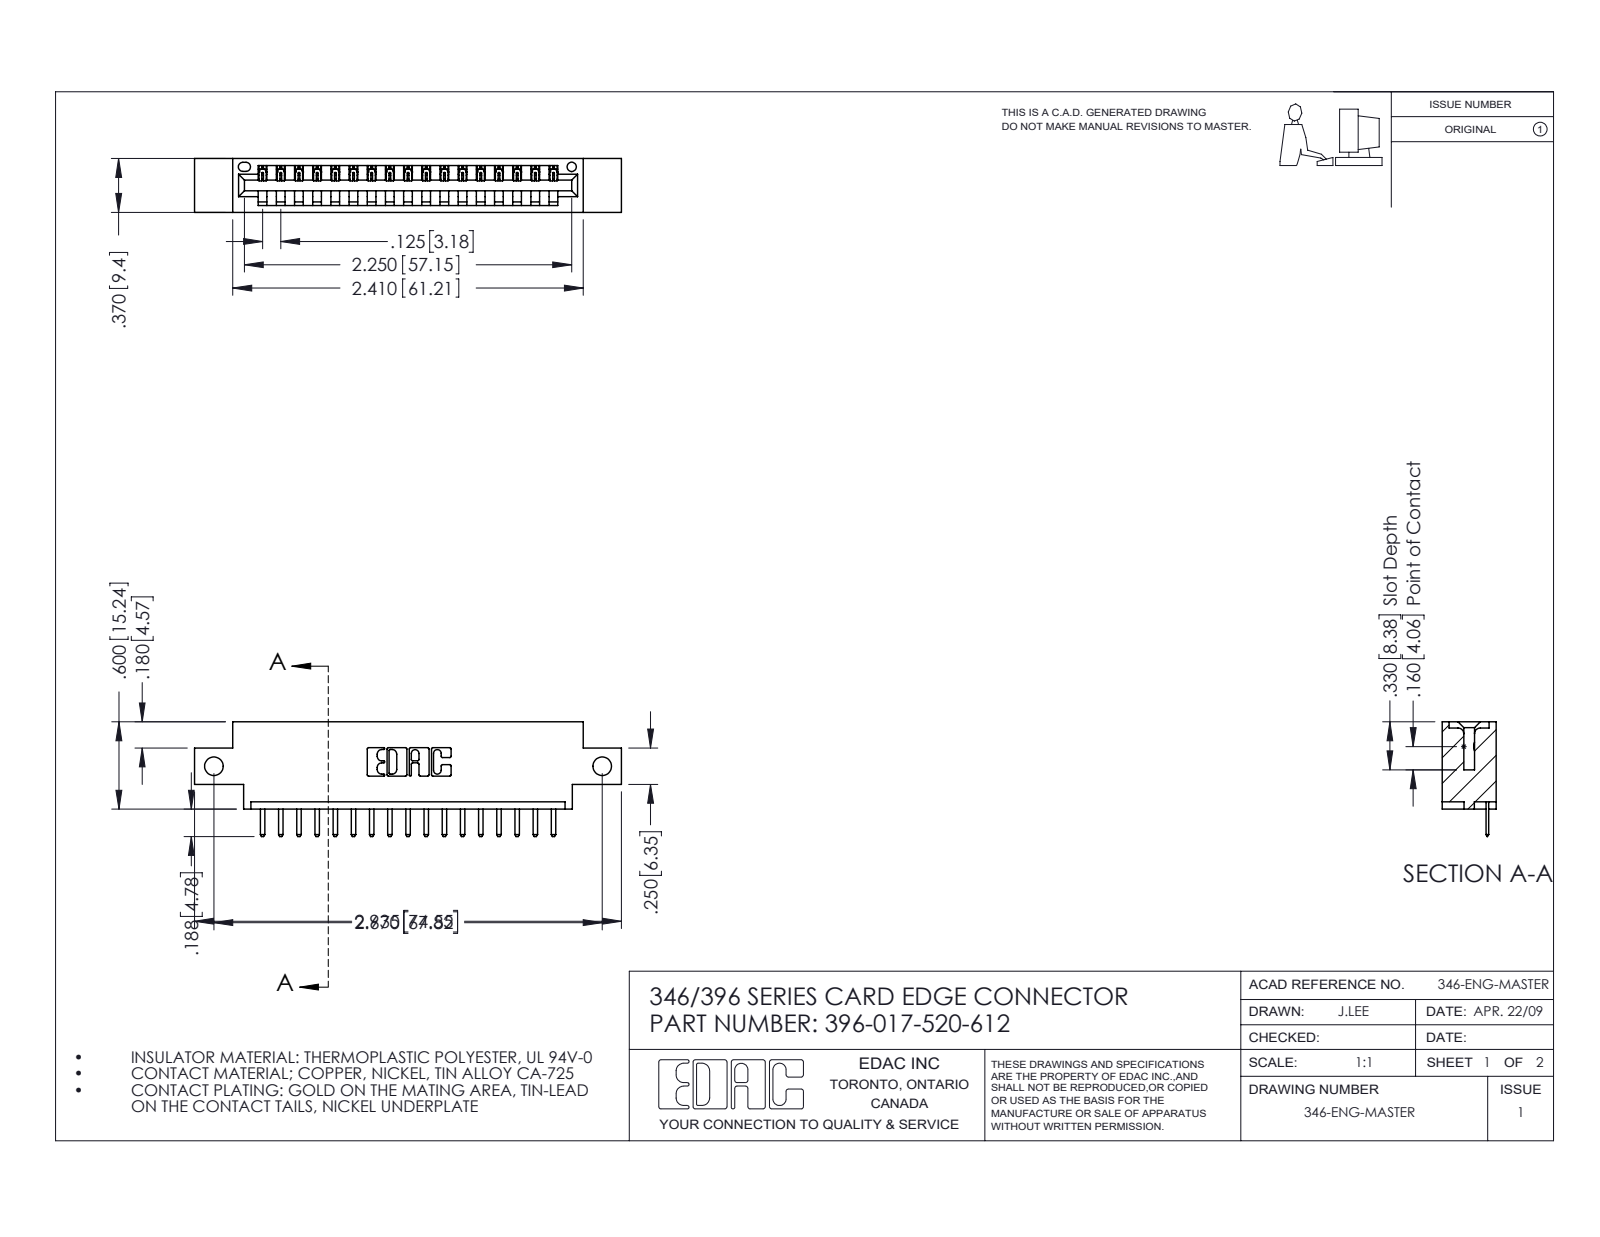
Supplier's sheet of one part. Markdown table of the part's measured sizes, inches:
| quantity | value |
| --- | --- |
| part name | 345-292-001_345-293-120; 396-017-520-612; 346 Part_0.170 Offset - Side Mount |
| STEP written by | SolidWorks 2016 (CONFIG_CONTROL_DESIGN) |
| units | inches |
| bodies | 18 solids, 1180 faces (794 planar, 386 cylindrical, 0 other) |
| overall size | 2.935 × 0.788 × 0.37 |
| volume | 0.407 in³ |
| surface area | 12.28 in² |
| round holes (diameter × count) | 0.128 × 2, 0.064 × 1 |
| partial cylindrical surfaces (radius × count) | 0.01 × 36, 0.006 × 34, 0.01 × 22, 0.007 × 6, 0.031 × 6, 0.026 × 3, 0.031 × 2, 0.04 × 2 |
| main face-to-face distances | 0.37, 0.048, 0.322, 0.25, 0.148, 0.222, 0.1, 0.174, 0.072, 0.298 |
| hole center spacings | 2.67 |
